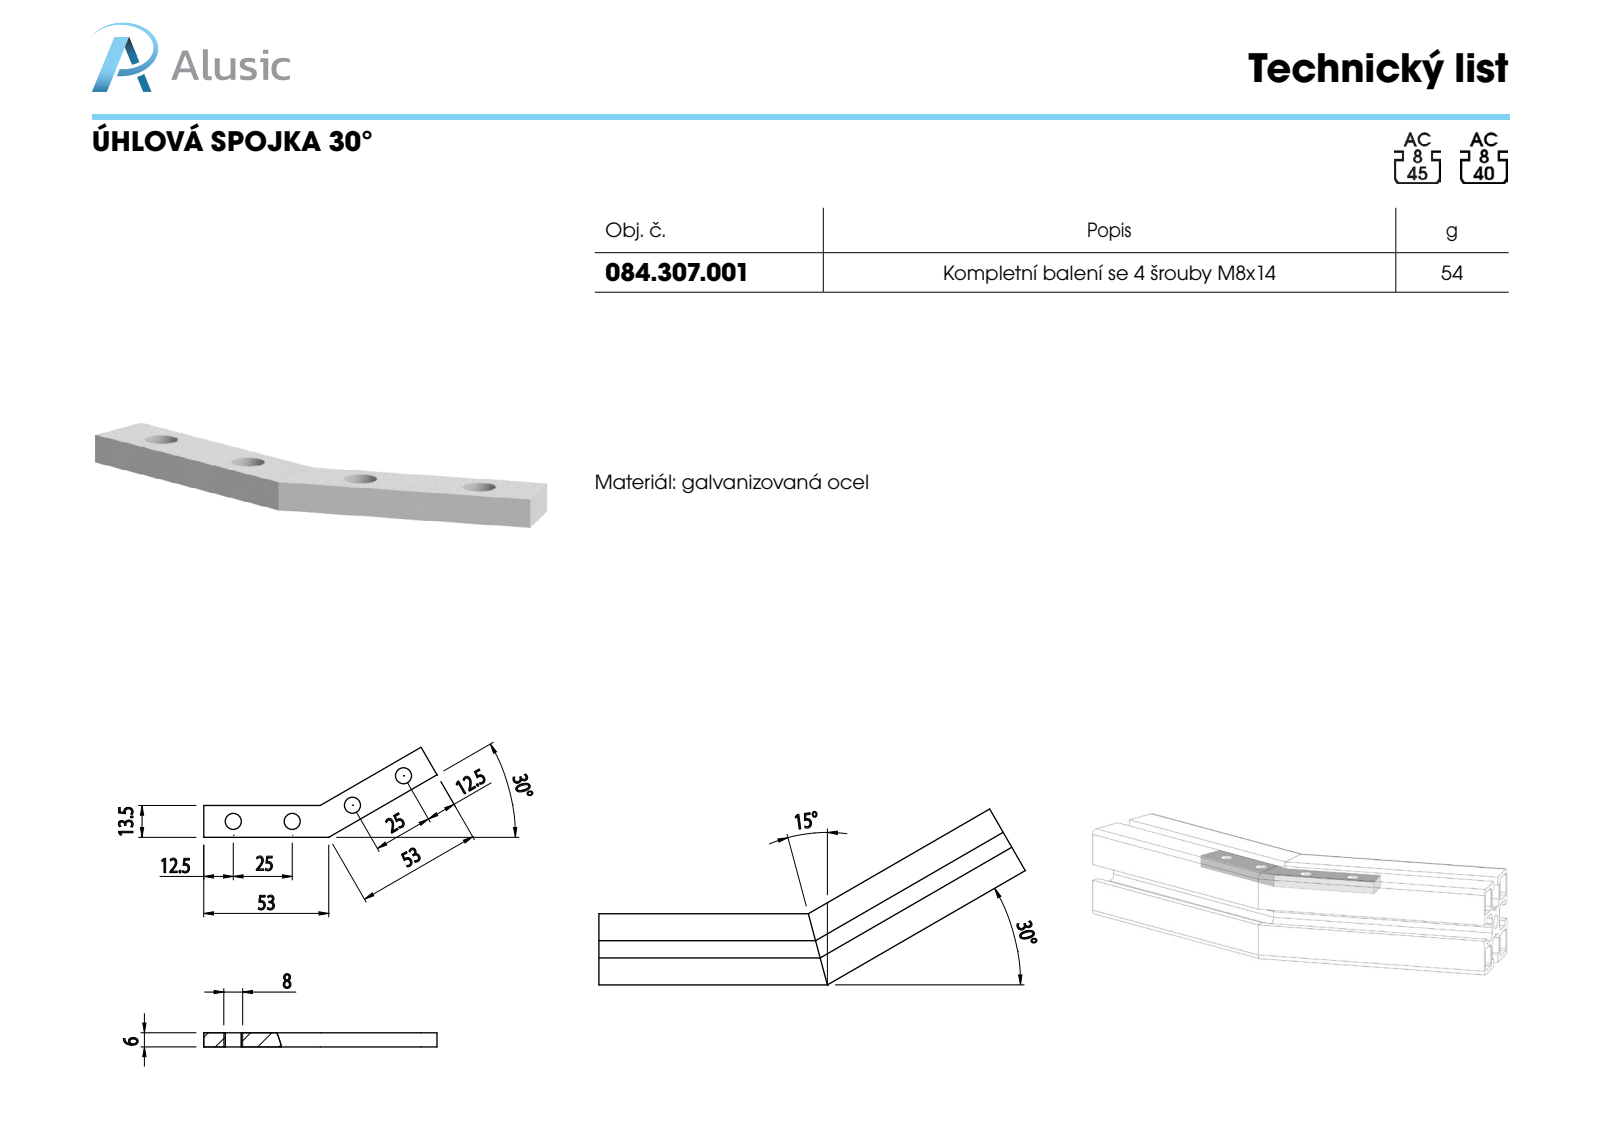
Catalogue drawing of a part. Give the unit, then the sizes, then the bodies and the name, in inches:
Units: inches
Overall size (bounding box): 3.894 × 1.504 × 0.236
Round holes (diameter × count): ⌀0.268 ×4
Main face-to-face distances: 0.236, 0.531
Hole centre spacings: 0.984, 2.008, 1.041, 2.943
Volume: 0.453 in³ · Surface area: 6.784 in²
Bodies: 1 solid, 16 faces (8 planar, 8 cylindrical, 0 other)
Part name (STEP PRODUCT): 084.307.001
STEP written by: SolidWorks 2011 (CONFIG_CONTROL_DESIGN)
